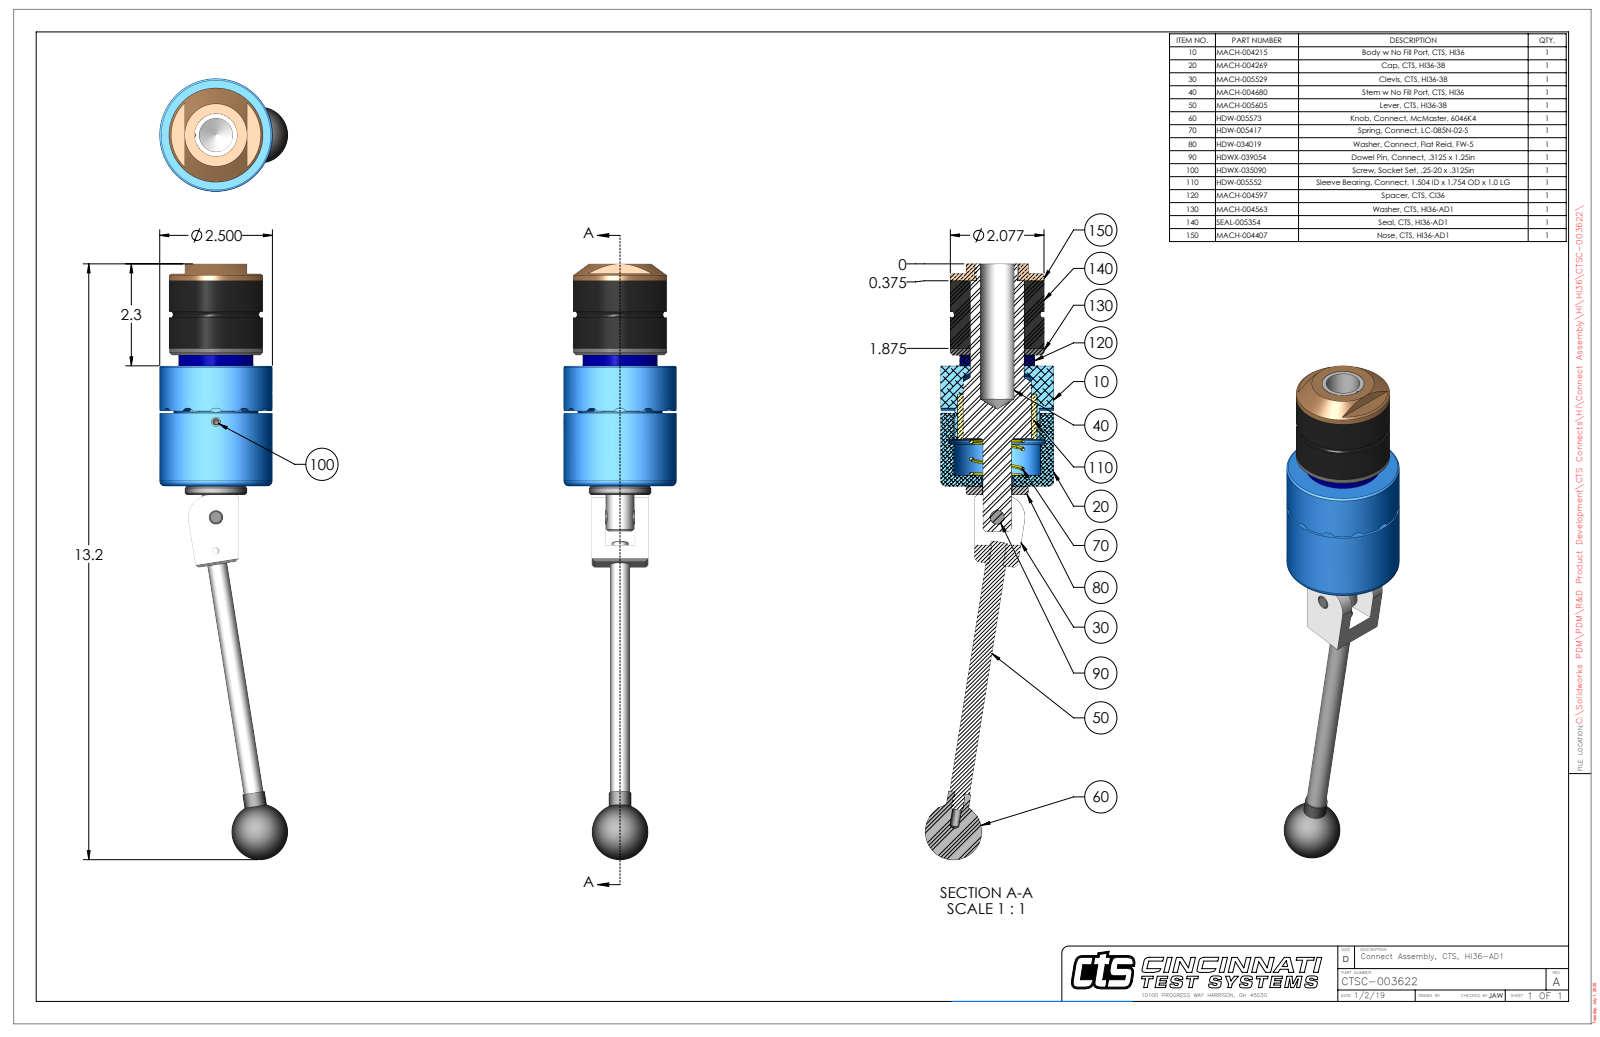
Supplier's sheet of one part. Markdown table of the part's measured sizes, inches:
| quantity | value |
| --- | --- |
| part name | CTSC-003622 |
| STEP written by | SolidWorks 2023 (AUTOMOTIVE_DESIGN) |
| units | inches |
| bodies | 10 solids, 271 faces (97 planar, 107 cylindrical, 67 other) |
| overall size | 13.215 × 2.843 × 2.5 |
| volume | 22.15 in³ |
| surface area | 122.3 in² |
| round holes (diameter × count) | 0.201 × 2, 0.15 × 1, 0.311 × 1, 0.313 × 1, 0.314 × 1, 0.656 × 1, 0.696 × 1, 0.75 × 1, 0.922 × 1, 1.188 × 1, 1.19 × 1, 1.195 × 1 |
| round bosses / shafts (diameter × count) | 2.5 × 1, 2.077 × 1, 1.875 × 1, 1.656 × 1, 1.38 × 1, 1.186 × 1, 1 × 1, 0.904 × 1 |
| partial cylindrical surfaces (radius × count) | 0.12 × 12, 0.029 × 2, 0.5 × 1, 1.183 × 1 |
| main face-to-face distances | 2.668, 4.555, 3.055, 1.5, 0.387, 1.887, 2.905, 0.237, 0.15, 1.65 |
| hole center spacings | 0.74, 2.118, 2.858 |
